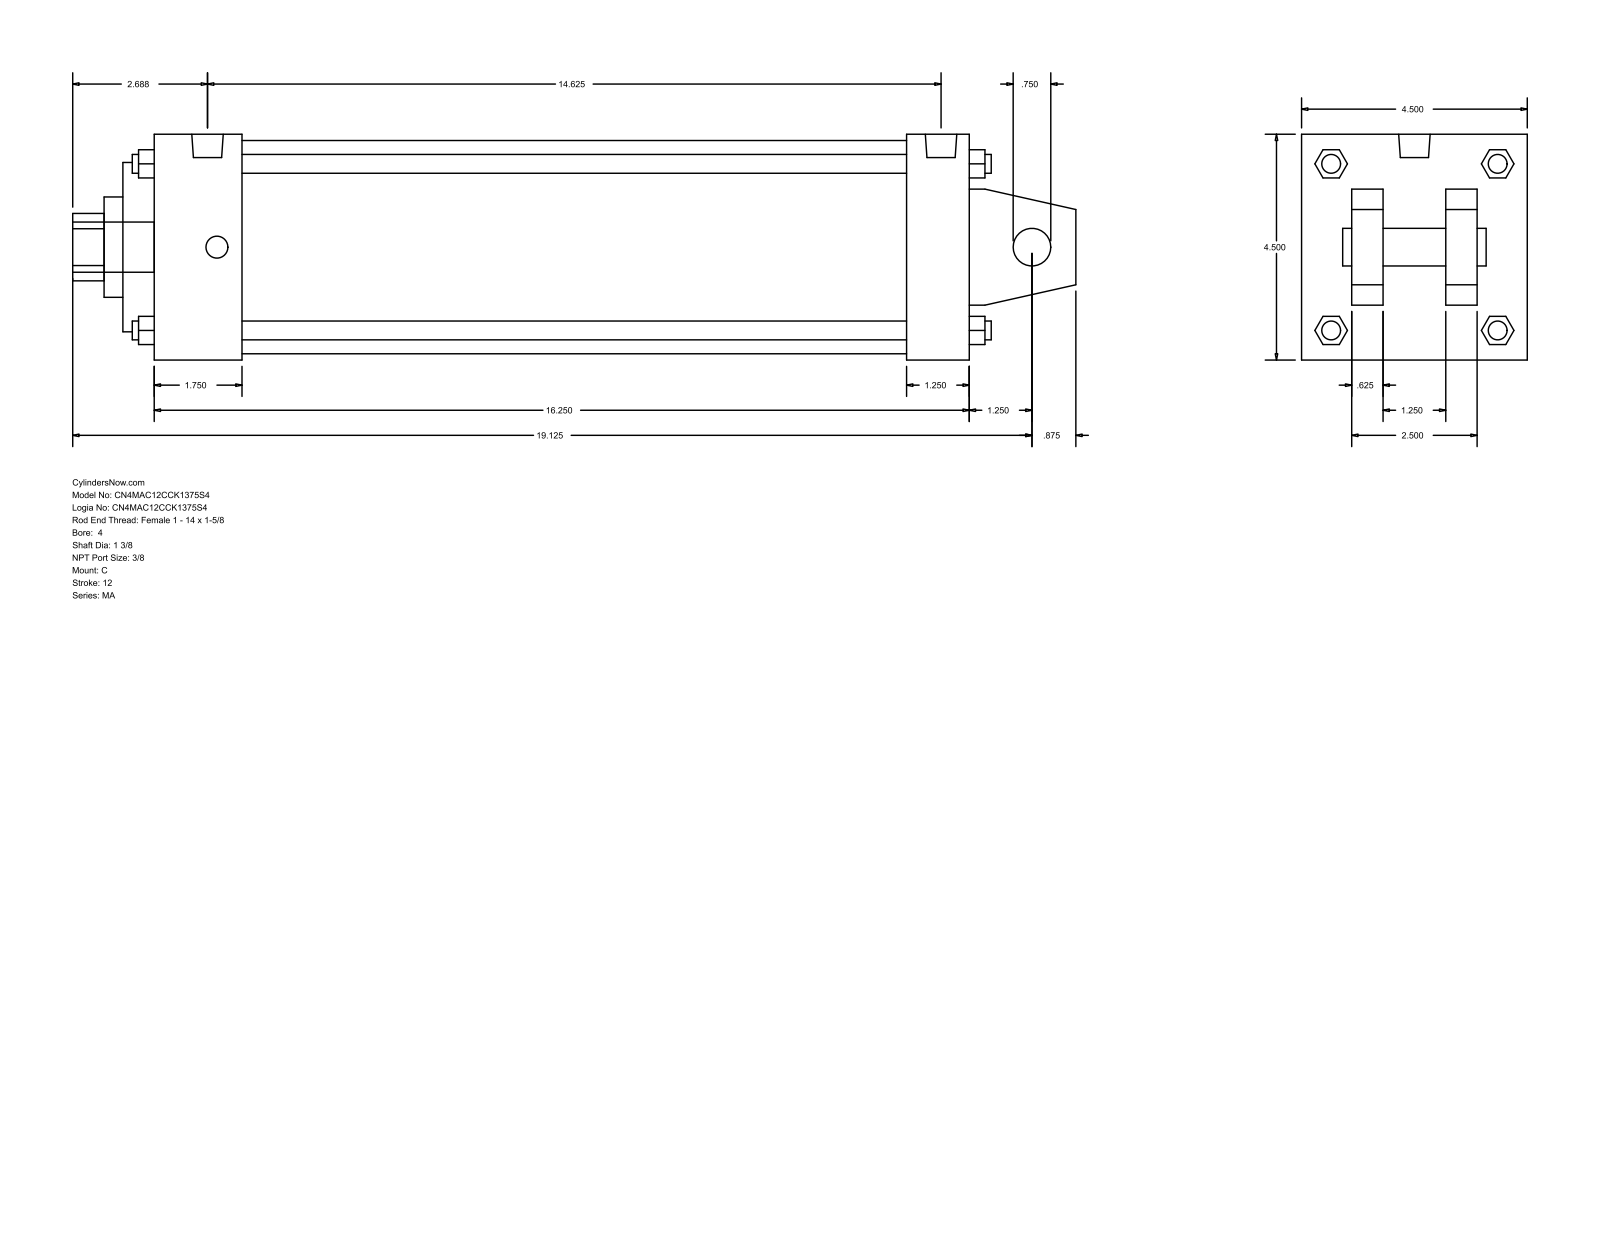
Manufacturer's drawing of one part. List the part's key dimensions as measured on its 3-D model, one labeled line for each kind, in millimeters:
Part name (STEP PRODUCT): MA_C__0400_1.375
STEP written by: GSSL Pune (CONFIG_CONTROL_DESIGN)
Units: millimetres
Bodies: 0 solids, 141 faces (109 planar, 32 cylindrical, 0 other)
Overall size (bounding box): 508 × 114.3 × 114.3
Round holes (diameter × count): ⌀19.05 ×1, ⌀34.92 ×1, ⌀50.8 ×1, ⌀85.72 ×1, ⌀107.95 ×1
Round bosses / shafts (diameter × count): ⌀11.11 ×4, ⌀9.53 ×4, ⌀15.93 ×2, ⌀25.4 ×1
Partial cylindrical surfaces — rounded edges, fillets, slot ends (radius × count): R17.06 ×1
Main face-to-face distances: 114.3, 15.87, 412.75, 73.03, 41.27, 25.4, 88.9, 47.63, 428.62, 396.87
